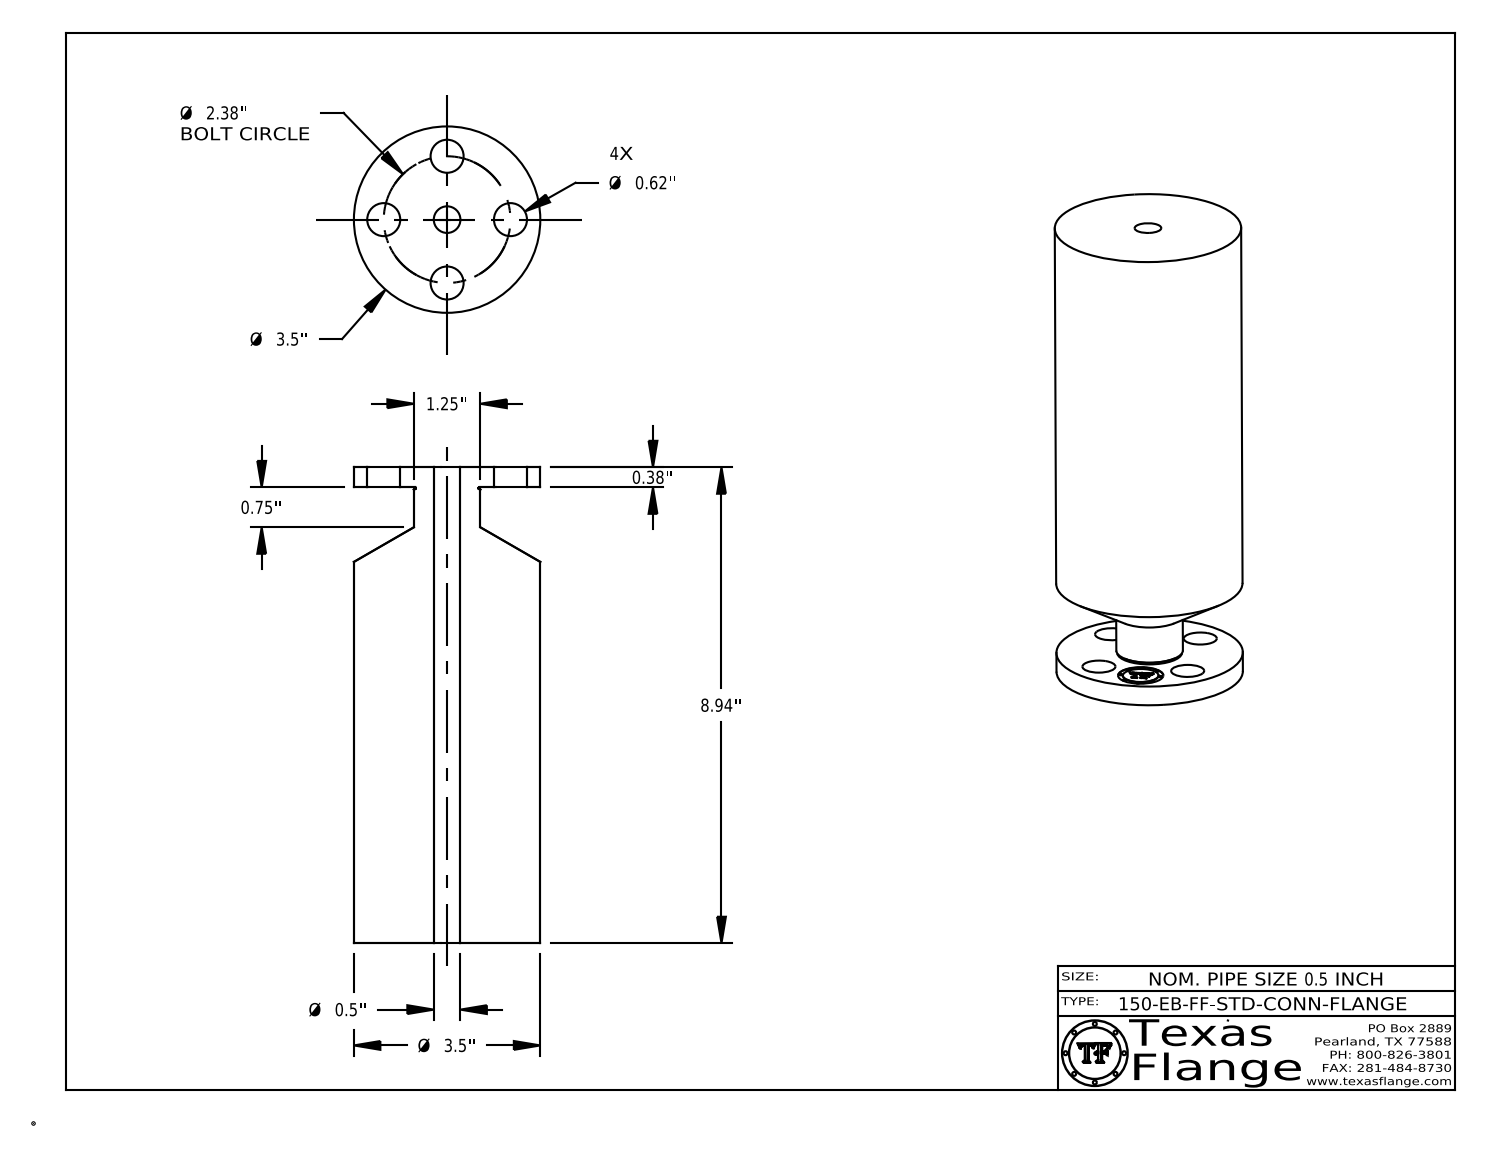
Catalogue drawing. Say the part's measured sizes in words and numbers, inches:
The part is named "0.5-150-EB-FF-STD-CONN-FLANGE". Its 3-D file was written by "CATIA V5 STEP AP214 (AUTOMOTIVE_DESIGN)". It is 1 solid with 410 faces: 368 planar, 36 cylindrical and 6 other. Overall it measures 8.938 by 3.5 by 3.5 inches. Its volume is 74.32 cubic inches and its surface area 137.5 square inches. Round holes: 4 of diameter 0.62, 1 of diameter 0.5, 1 of diameter 0.85. Round bosses or shafts: 8 of diameter 0.051, 1 of diameter 3.5, 1 of diameter 1.25, 1 of diameter 0.67. The main face-to-face distances are 8.937, 0.378, 8.56, 0.372, 8.565, 0.254, 0.248, 0.016, 0.046, 0.165. The hole center spacings are 1.19, 1.683, 0.911, 2.199, 2.38, 1.19.
